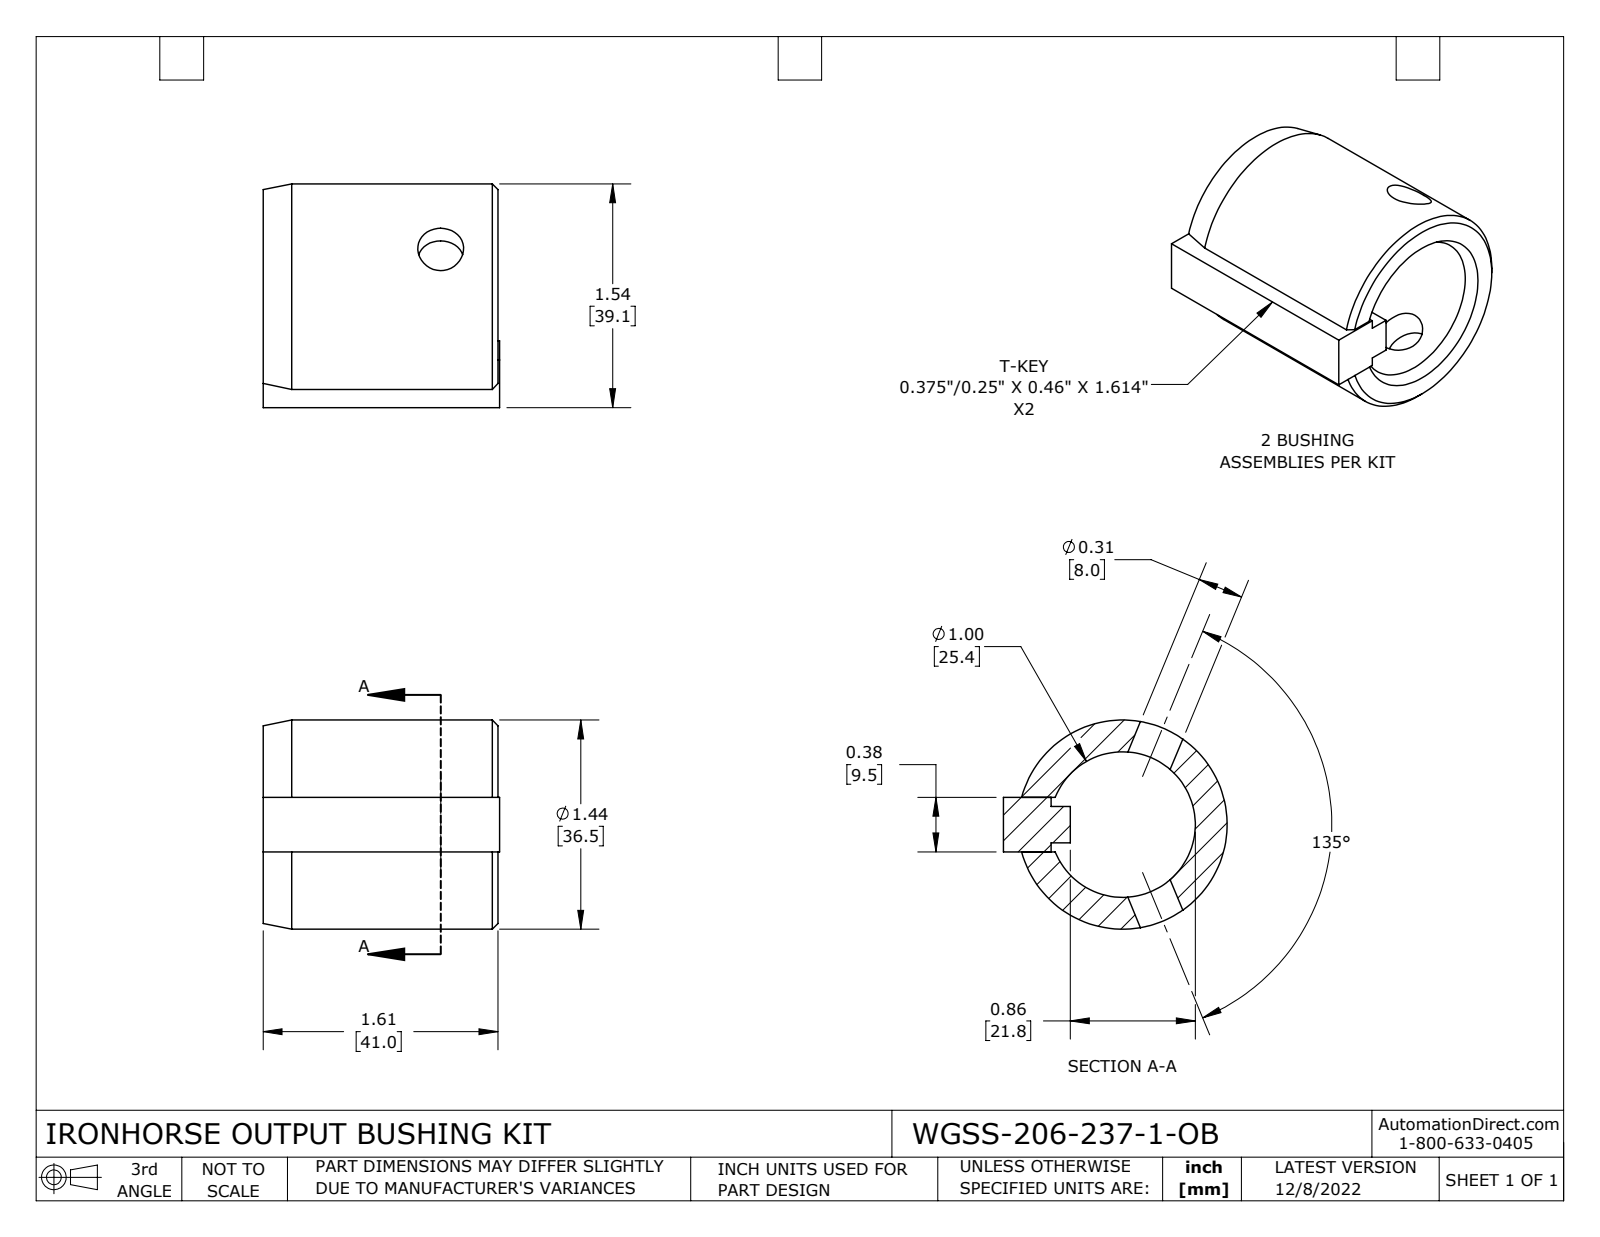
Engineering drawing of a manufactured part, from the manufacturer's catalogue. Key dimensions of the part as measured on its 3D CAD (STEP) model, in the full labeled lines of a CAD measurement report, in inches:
Part name (STEP PRODUCT): WGSS-206-237-1-OB
STEP written by: SolidWorks 2021 (CONFIG_CONTROL_DESIGN)
Units: inches
Bodies: 2 solids, 35 faces (14 planar, 10 cylindrical, 11 other)
Overall size (bounding box): 1.625 × 1.537 × 1.437
Volume: 1.407 in³ · Surface area: 16.08 in²
Round holes (diameter × count): ⌀0.315 ×2, ⌀1 ×1
Round bosses / shafts (diameter × count): ⌀1.437 ×1
Main face-to-face distances: 0.375, 1.614, 0.46, 0.062, 0.312, 0.25, 0.313, 0.063, 0.133, 0.327
